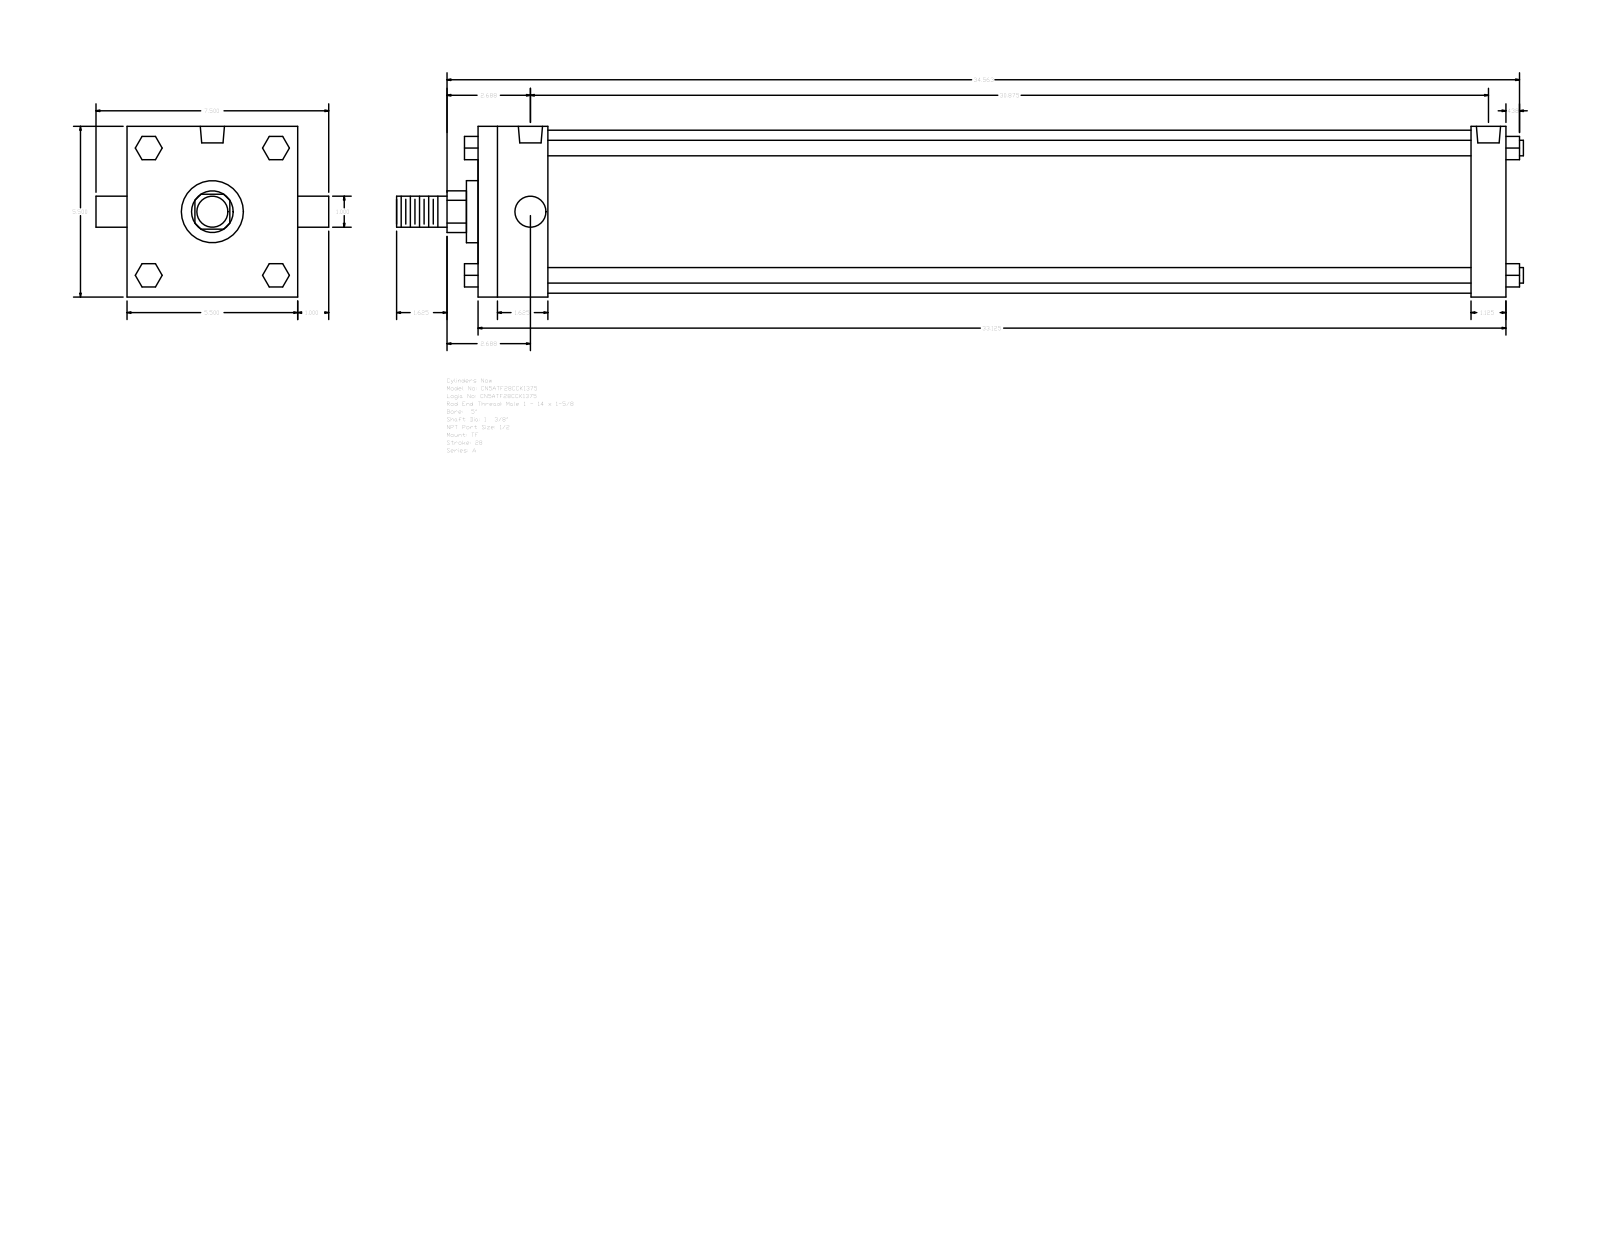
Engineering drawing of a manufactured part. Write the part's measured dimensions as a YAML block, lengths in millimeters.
part_name: "A_TF__0500_1.375"
step_written_by: "GSSL Pune (CONFIG_CONTROL_DESIGN)"
units: millimeters
bodies: {solids: 0, faces: 120, planar: 92, cylindrical: 28, other: 0}
overall_size: [922.34, 190.5, 139.7]
round_holes:
  - {diameter: 8.73, count: 3}
  - {diameter: 19.77, count: 2}
round_bosses_or_shafts:
  - {diameter: 12.7, count: 4}
  - {diameter: 25.4, count: 2}
  - {diameter: 133.35, count: 1}
  - {diameter: 50.8, count: 1}
  - {diameter: 34.92, count: 1}
partial_cylinders:
  - {radius: 17.06, count: 1}
face_to_face_distances: [139.7, 841.37, 57.15, 812.8, 28.57, 755.65, 784.22, 19.05, 52.07, 90.18]
hole_center_spacings: [2.39, 781.84, 779.45, 784.23]
